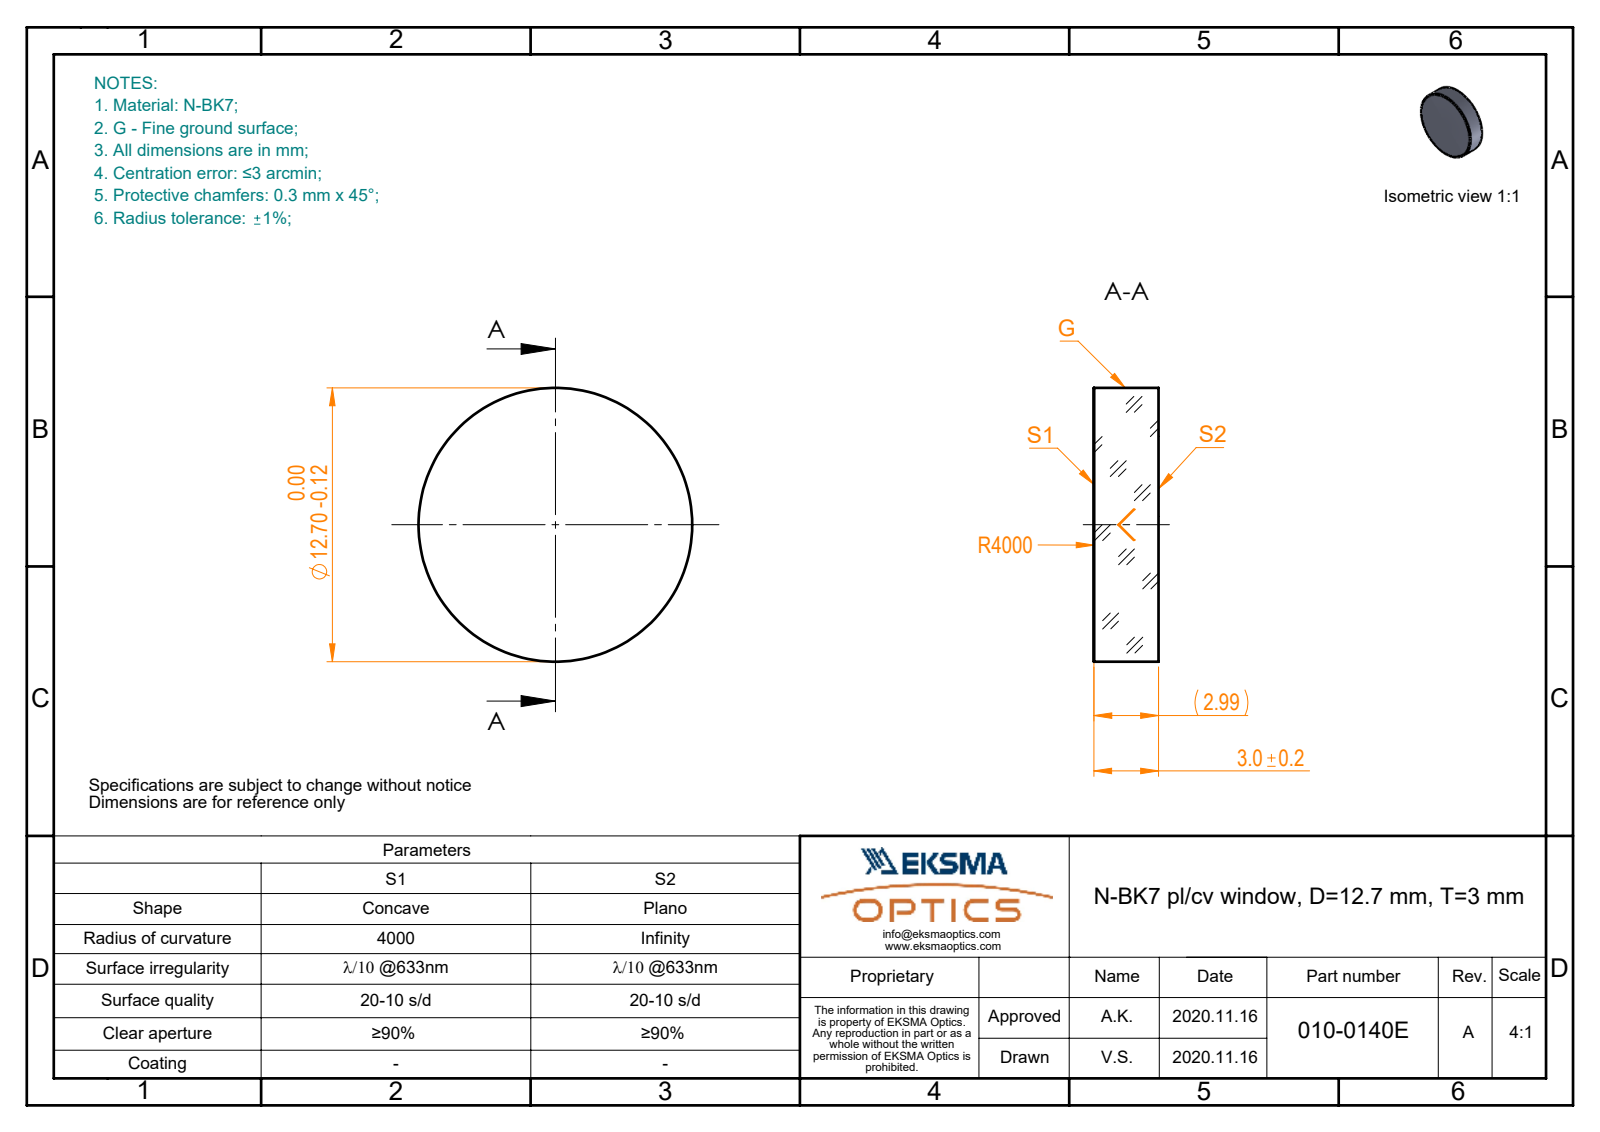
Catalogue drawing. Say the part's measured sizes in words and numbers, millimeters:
The part is named "010-0140E_N-BK7_PCV_window". Its 3-D file was written by "SolidWorks 2019 (CONFIG_CONTROL_DESIGN)". It is 1 solid with 5 faces: 1 planar, 2 cylindrical and 2 other. Overall it measures 12.7 by 12.7 by 3 millimeters. Its volume is 380 cubic millimeters and its surface area 373 square millimeters. Round bosses or shafts: 1 of diameter 12.7.
